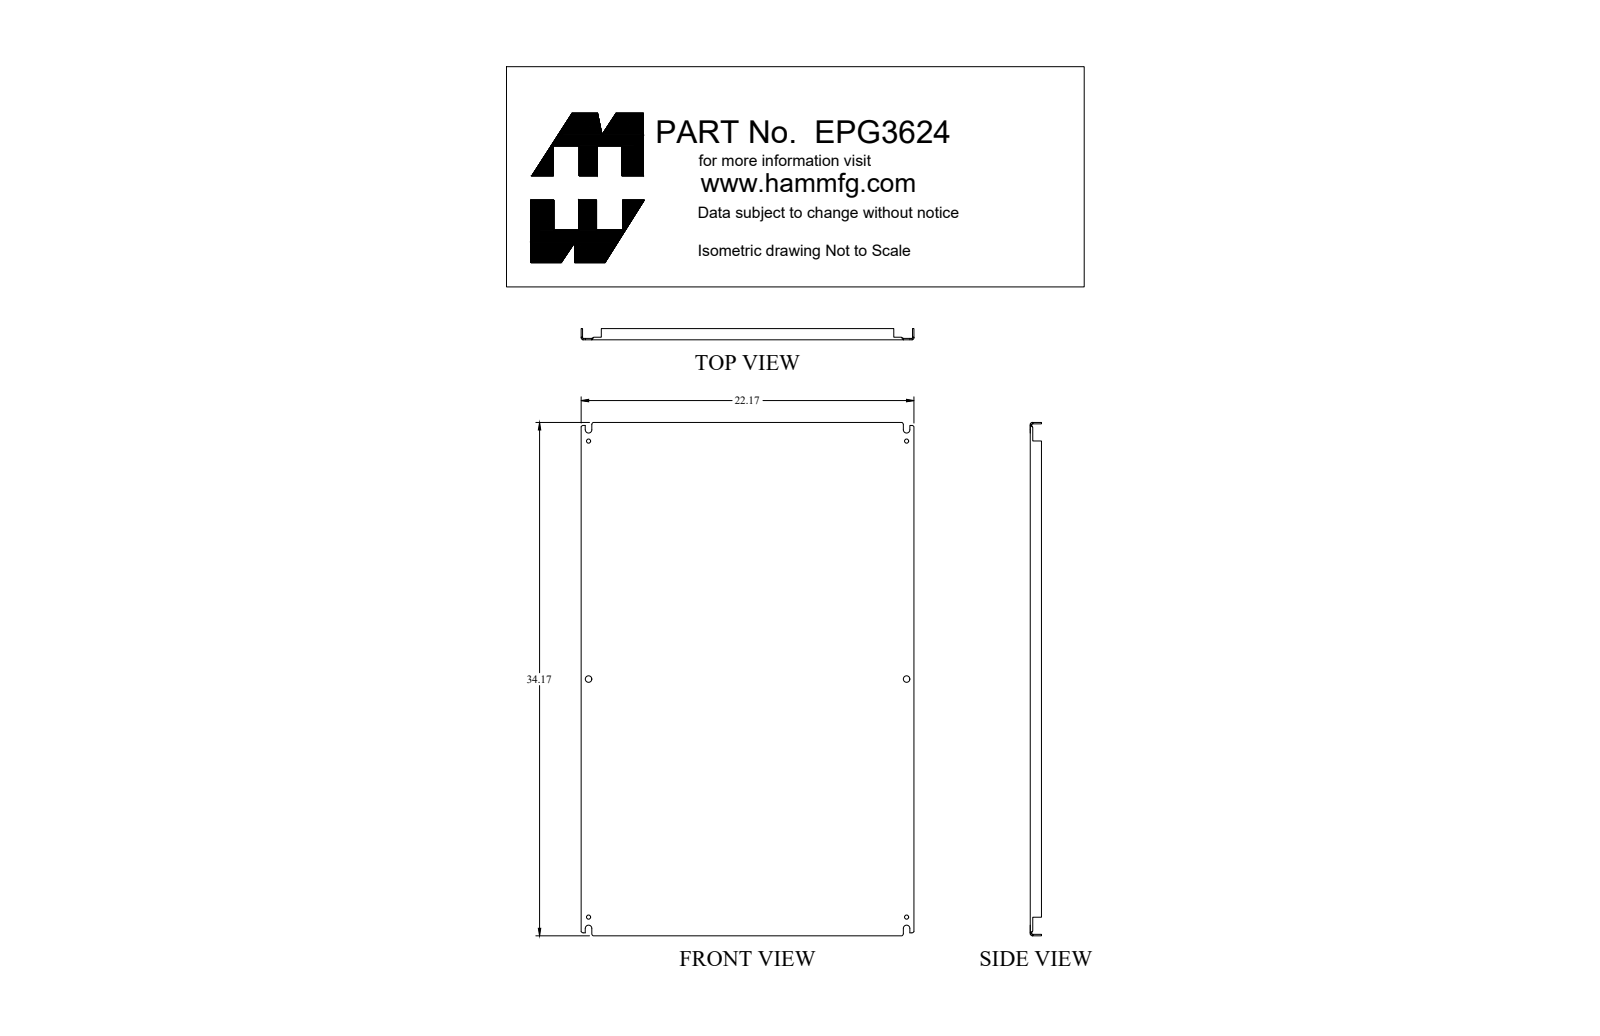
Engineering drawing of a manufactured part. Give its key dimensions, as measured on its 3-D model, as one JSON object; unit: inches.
{"part_name": "EPG3624", "step_written_by": "SolidWorks 2018 (AUTOMOTIVE_DESIGN)", "units": "inches", "bodies": {"solids": 1, "faces": 132, "planar": 74, "cylindrical": 42, "other": 16}, "overall_size": [34.17, 22.17, 0.75], "volume_in3": 77.76, "surface_area_in2": 1649, "round_holes": [[0.281, 4], [0.437, 2]], "partial_cylinders_radius": [[0.048, 4], [0.063, 4], [0.143, 4], [0.219, 4]], "face_to_face_distances": [0.095, 22.075, 34.075, 21.98, 22.17, 33.98, 34.17, 0.75, 0.655, 0.171], "hole_center_spacings": [15.844, 26.457, 21.188, 31.688, 38.119]}
